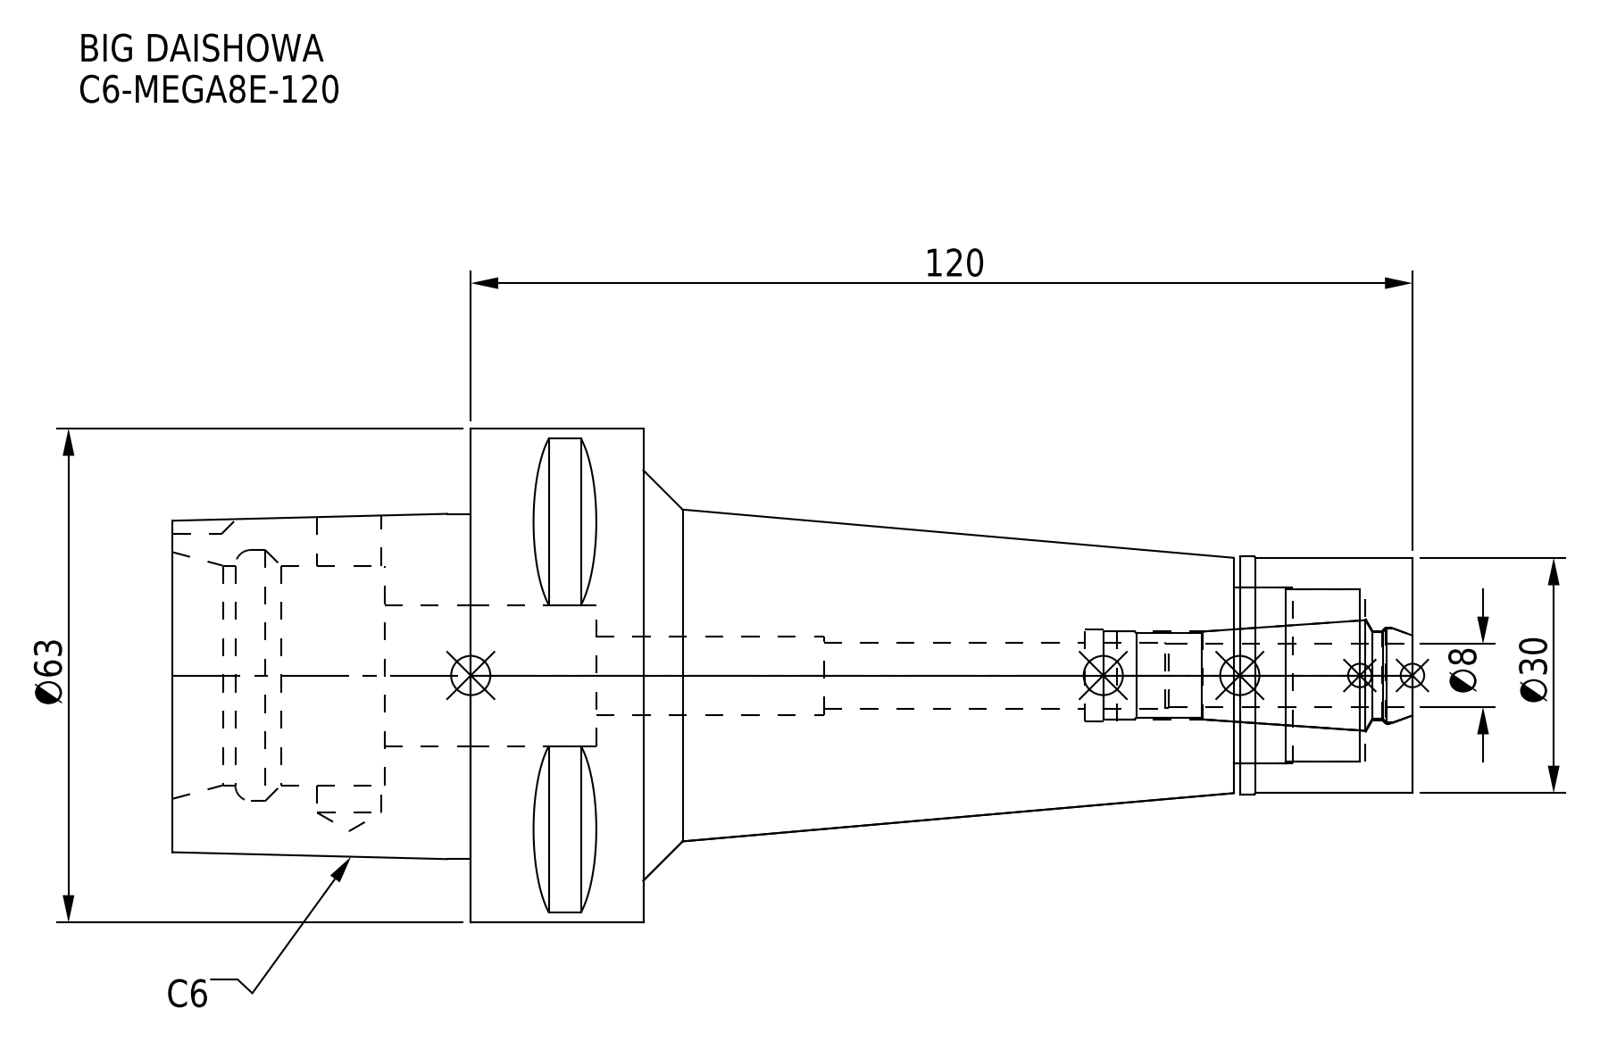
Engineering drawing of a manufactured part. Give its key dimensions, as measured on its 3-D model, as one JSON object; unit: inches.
{"part_name": "MEN8_1.stp; C6-MEGA8E-120-080_ASM.stp; C6-MEGA8E-120_1.stp; DXF_TEMP_ASSY_ASM_4_ASM.stp (+3 more)", "step_written_by": "SolidWorks 2019 (CONFIG_CONTROL_DESIGN)", "units": "inches", "bodies": {"solids": 2, "faces": 100, "planar": 37, "cylindrical": 39, "other": 24}, "overall_size": [6.22, 2.48, 2.48], "volume_in3": 11.28, "surface_area_in2": 56.57, "round_holes": [[0.319, 1], [0.331, 1], [0.394, 1], [0.441, 1], [0.449, 1], [0.465, 1], [0.484, 1], [0.709, 1], [0.866, 1], [0.886, 1], [1.102, 1], [1.26, 1]], "round_bosses_or_shafts": [[2.48, 1], [1.193, 1], [1.181, 1]], "partial_cylinders_radius": [[0.197, 1]], "face_to_face_distances": [0.866, 3.858, 4.724, 1.063, 6.22, 2.362, 1.496, 0.236, 0.63, 5.157]}
